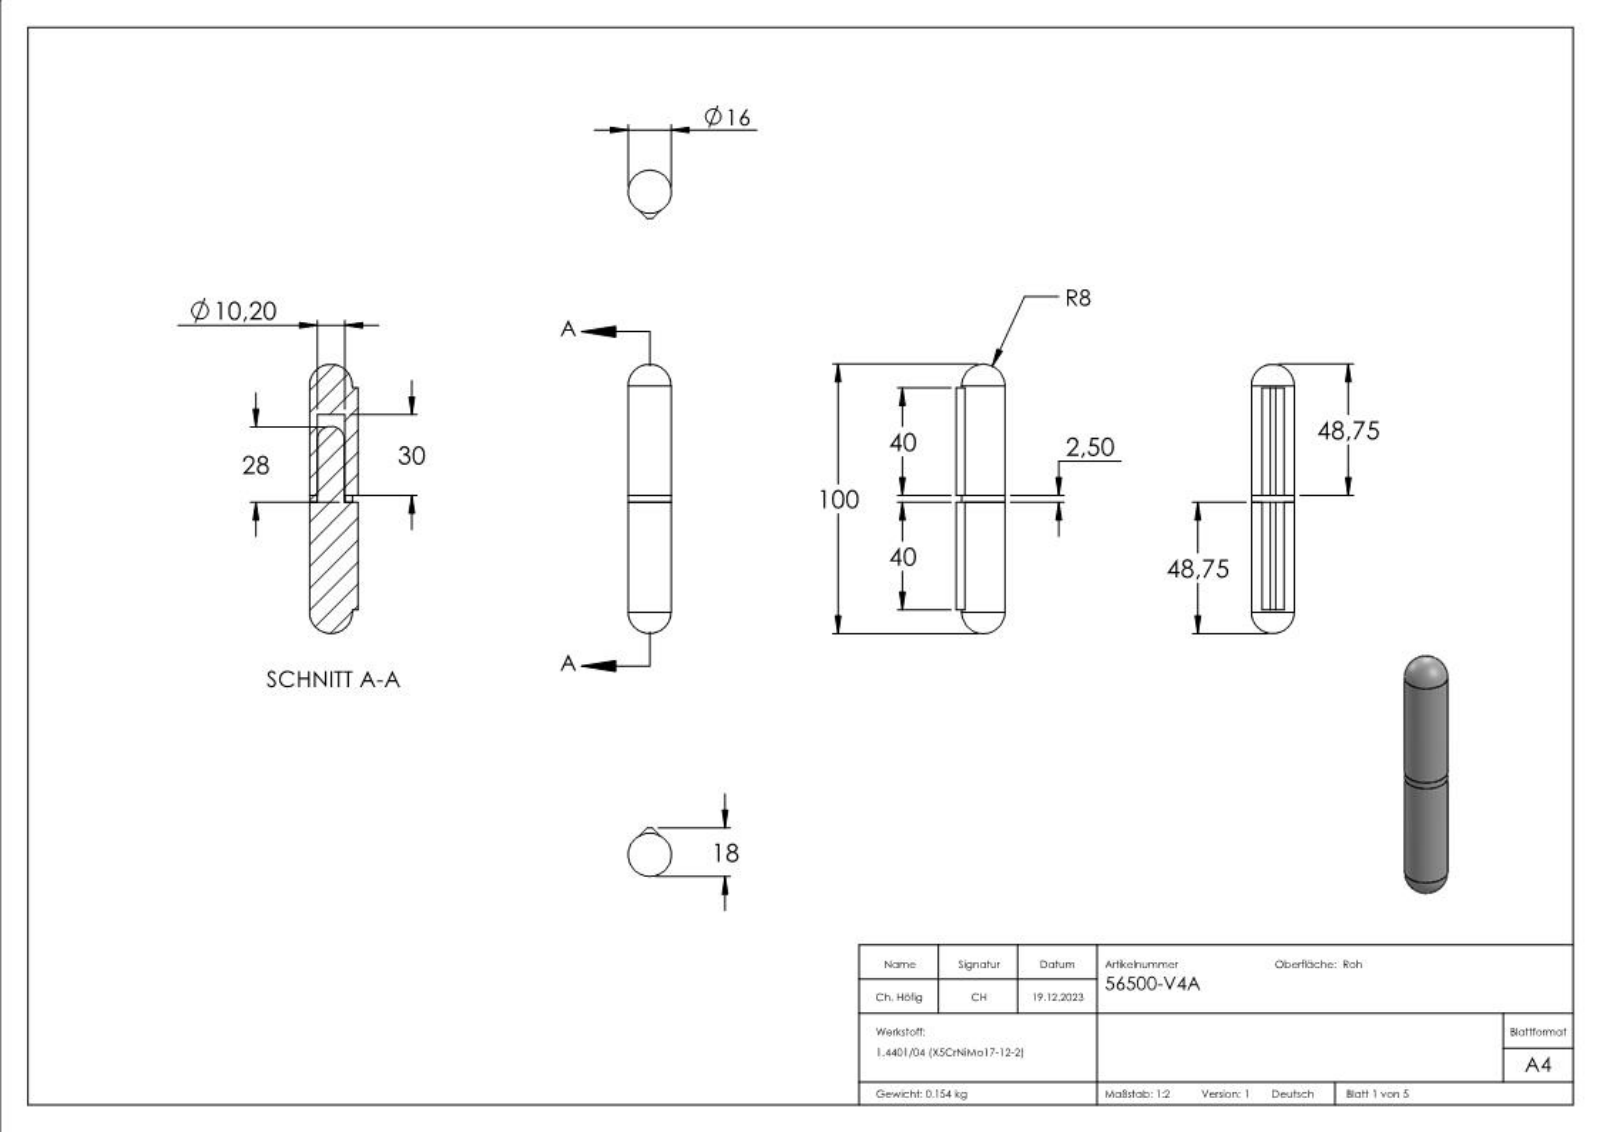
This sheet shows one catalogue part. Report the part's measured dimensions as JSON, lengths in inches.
{"part_name": "56500-V4A Teil1_56500-V4A Teil1; 56500-V4A Teil3_56500-V4A Teil3; 56500-V4A Teil2_56500-V4A Teil2; 56500-V4A", "step_written_by": "SolidWorks 2018 (CONFIG_CONTROL_DESIGN)", "units": "inches", "bodies": {"solids": 3, "faces": 242, "planar": 142, "cylindrical": 6, "other": 94}, "overall_size": [3.937, 0.709, 0.63], "volume_in3": 1.172, "surface_area_in2": 11.97, "round_holes": [[0.402, 1], [0.409, 1]], "round_bosses_or_shafts": [[0.63, 1], [0.394, 1]], "face_to_face_distances": [0.098, 1.28, 1.181, 1.575, 1.673, 2.854, 3.248, 0.394, 1.677, 0.102]}
